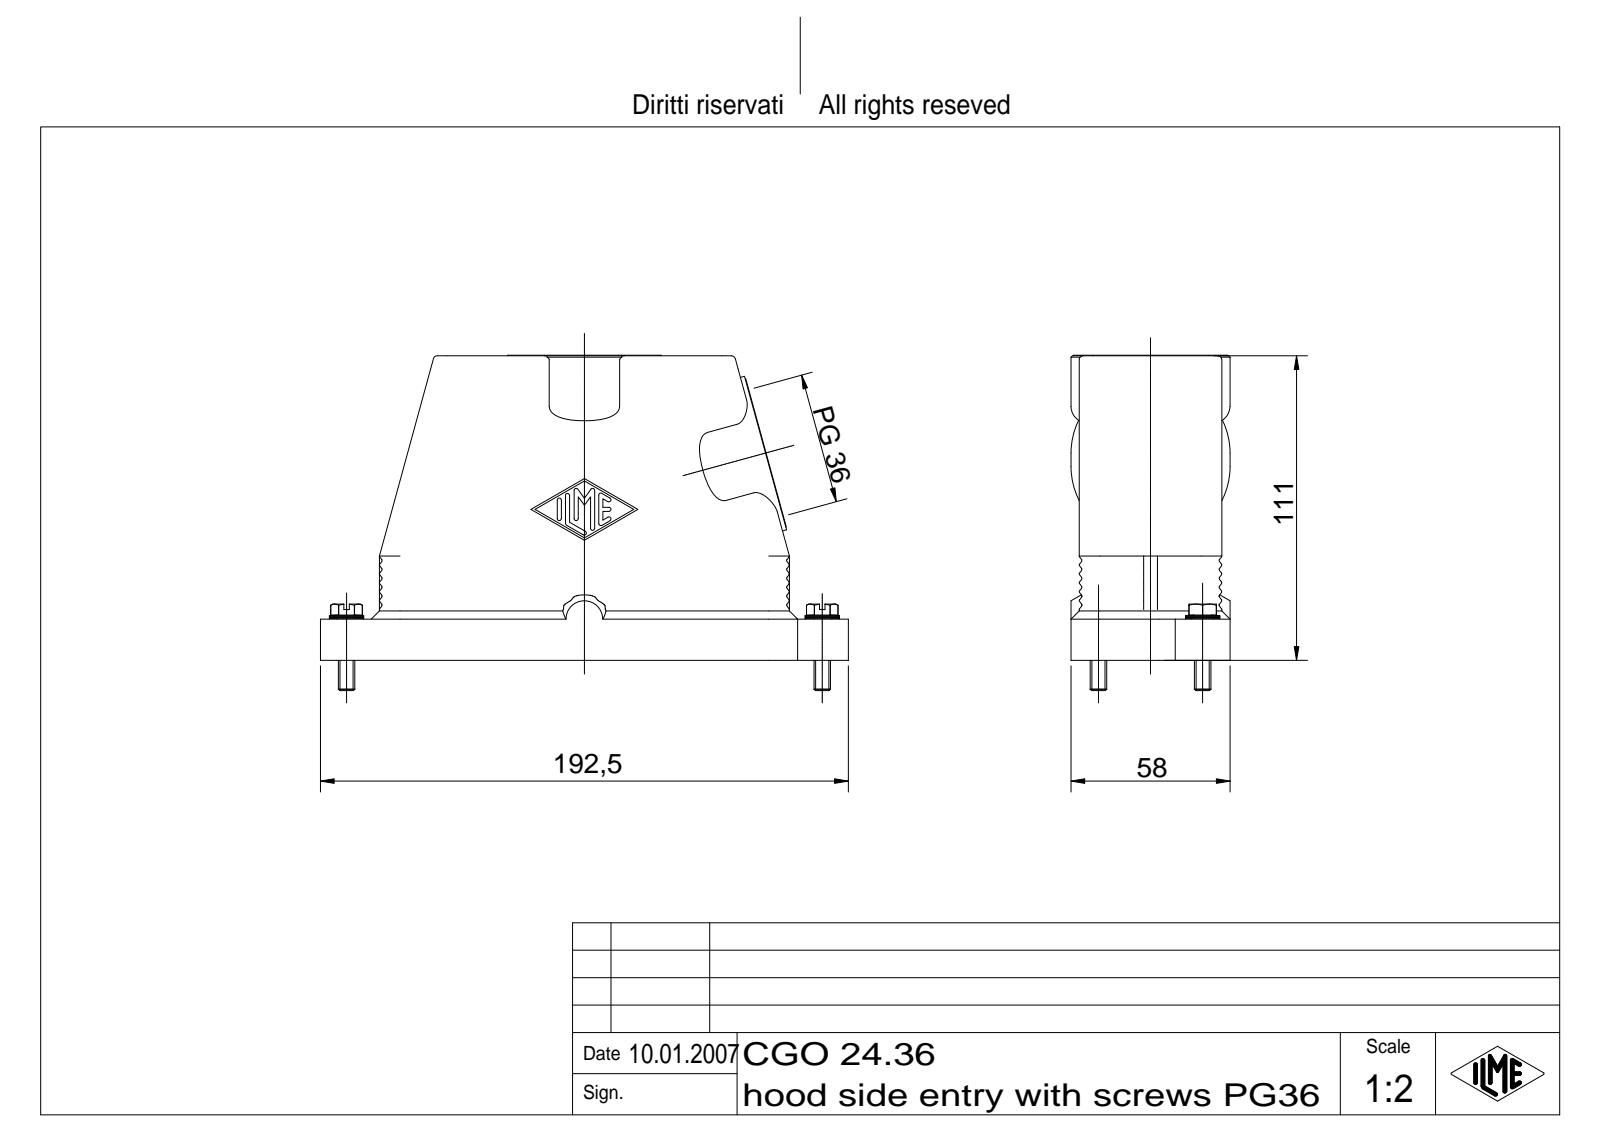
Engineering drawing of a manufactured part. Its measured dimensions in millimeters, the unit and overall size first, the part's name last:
Units: millimetres
Overall size (bounding box): 192.5 × 122.2 × 58
Round holes (diameter × count): ⌀2.46 ×2, ⌀3.2 ×2, ⌀6.6 ×2, ⌀15 ×2, ⌀45.48 ×1
Round bosses / shafts (diameter × count): ⌀58 ×2, ⌀56 ×2, ⌀12.5 ×2, ⌀6 ×2
Partial cylindrical surfaces — rounded edges, fillets, slot ends (radius × count): R0.5 ×39, R0.75 ×14, R7.5 ×8, R6 ×6, R1.5 ×4, R3 ×4, R5.75 ×2, R10.5 ×2
Main face-to-face distances: 3, 52, 49, 46, 6, 55, 2.5, 0.5, 58, 3.5
Hole centre spacings: 35.18, 142.51, 107.45, 177.61
Volume: 236 116 mm³ · Surface area: 106 901 mm²
Bodies: 3 solids, 767 faces (189 planar, 195 cylindrical, 383 other)
Part name (STEP PRODUCT): CGO 24.36
STEP written by: Autodesk Inventor 7 (AUTOMOTIVE_DESIGN)
